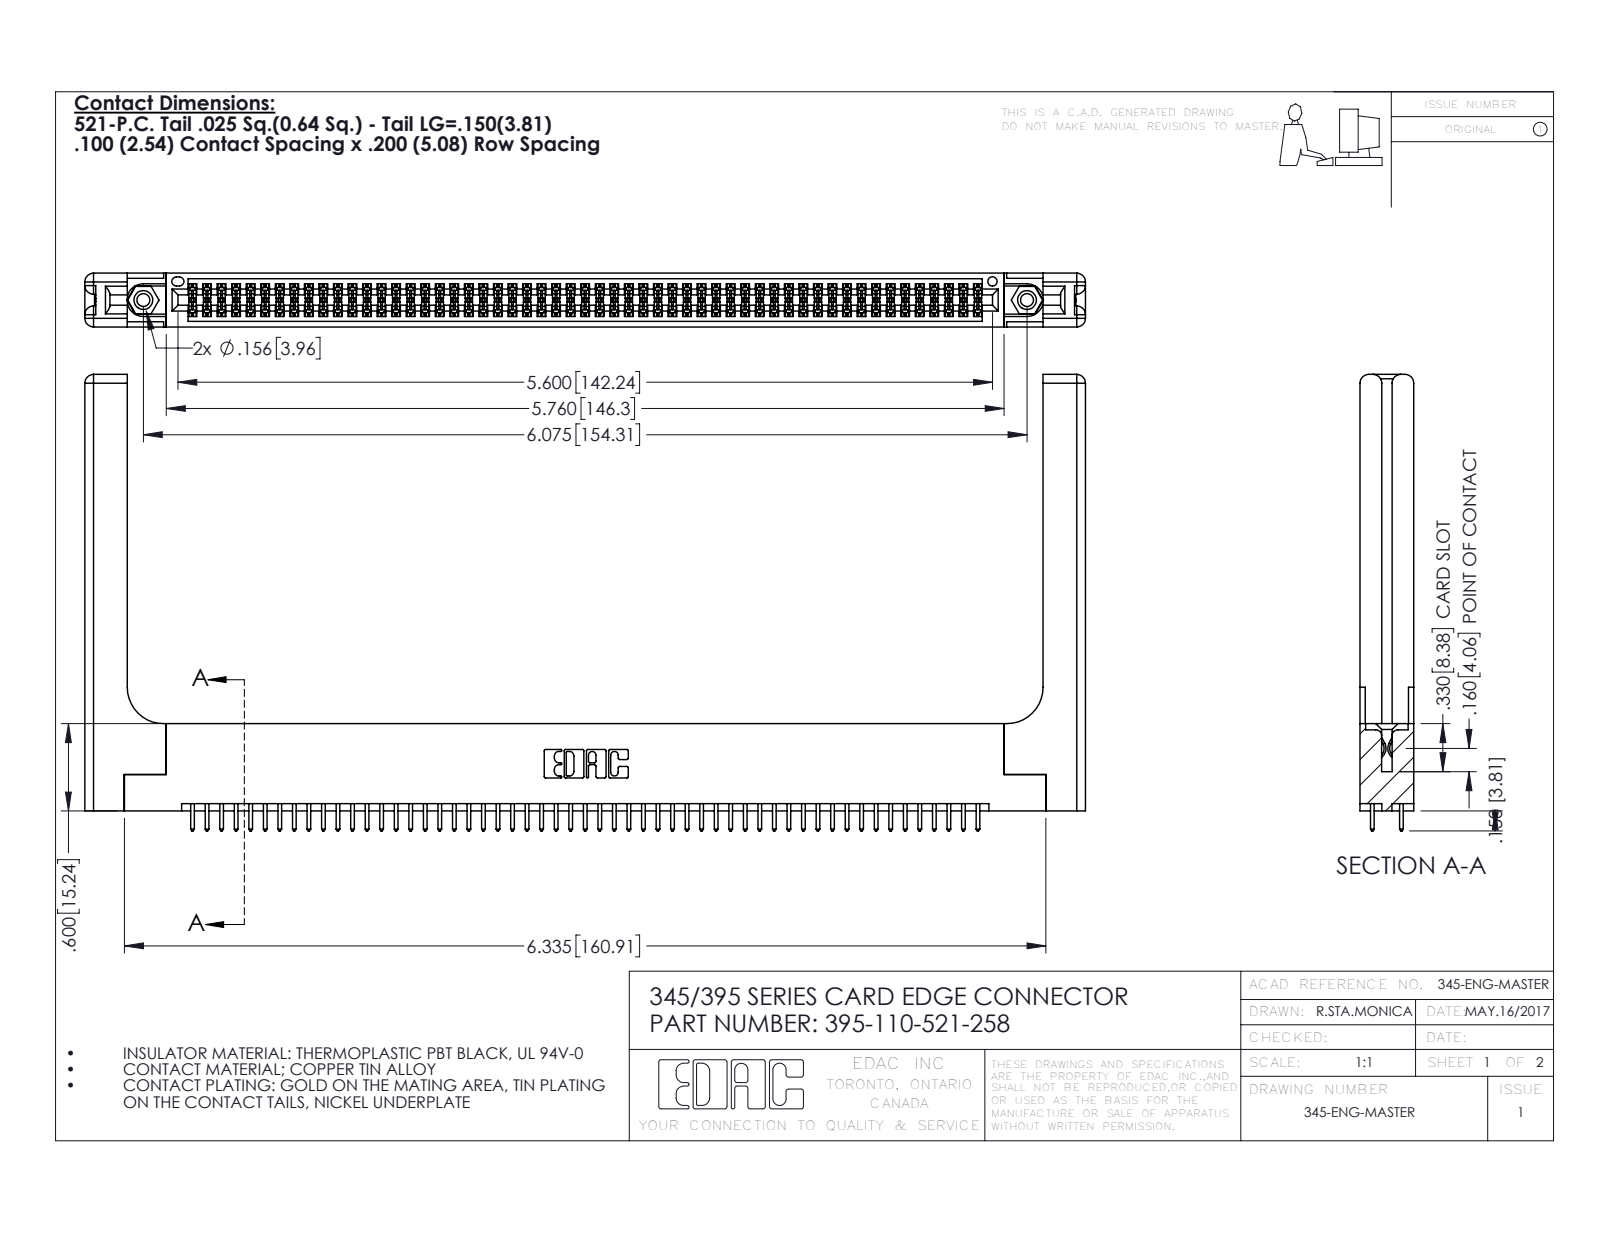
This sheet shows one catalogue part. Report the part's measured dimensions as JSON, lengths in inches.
{"part_name": "345-292-001_345-293-121; 345-220-058_345-220-058; 345-250-001_345-250-001-102; 345 Part_Flush Mounting Lugs - 0.156 Dia-TH (+1 more)", "step_written_by": "SolidWorks 2016 (CONFIG_CONTROL_DESIGN)", "units": "inches", "bodies": {"solids": 115, "faces": 5882, "planar": 3858, "cylindrical": 1964, "other": 60}, "overall_size": [6.879, 3.137, 0.37], "volume_in3": 1.558, "surface_area_in2": 46.84, "round_holes": [[0.089, 2], [0.125, 2], [0.156, 2], [0.064, 1]], "round_bosses_or_shafts": [[0.155, 2]], "partial_cylinders_radius": [[0.006, 165], [0.01, 110], [0.01, 22], [0.06, 16], [0.007, 6], [0.031, 6], [0.026, 3], [0.014, 2]], "face_to_face_distances": [0.072, 0.298, 0.37, 0.2, 0.098, 0.272, 0.025, 0.225, 0.175, 0.148], "hole_center_spacings": [0.27, 5.839, 6.075]}
